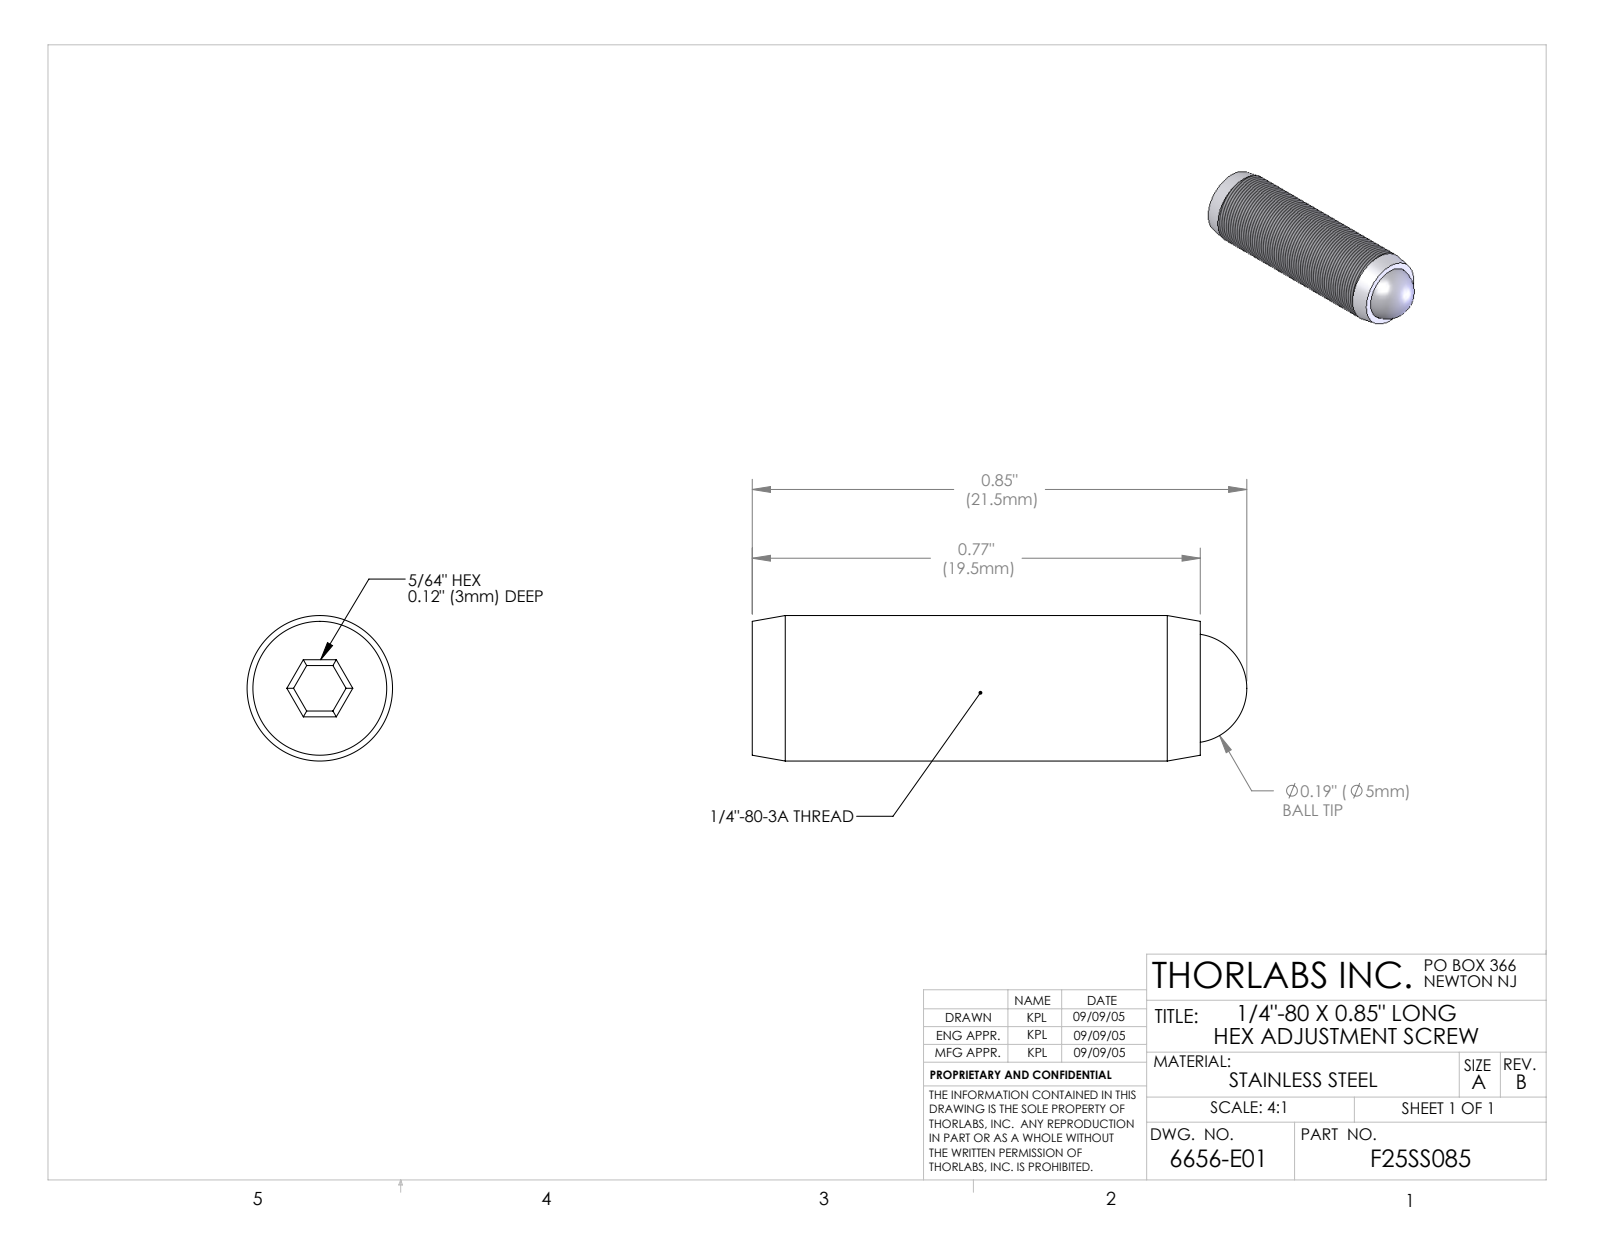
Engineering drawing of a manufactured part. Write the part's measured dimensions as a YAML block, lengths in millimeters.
part_name: "6656-E0W"
step_written_by: "SolidWorks 2007 (AUTOMOTIVE_DESIGN)"
units: millimeters
bodies: {solids: 2, faces: 29, planar: 15, cylindrical: 4, other: 10}
overall_size: [21.59, 6.35, 6.35]
volume: 620
surface_area: 561
round_holes:
  - {diameter: 4.78, count: 1}
round_bosses_or_shafts:
  - {diameter: 6.35, count: 1}
face_to_face_distances: [19.56, 1.99, 3.05, 16.51, 1.98]
